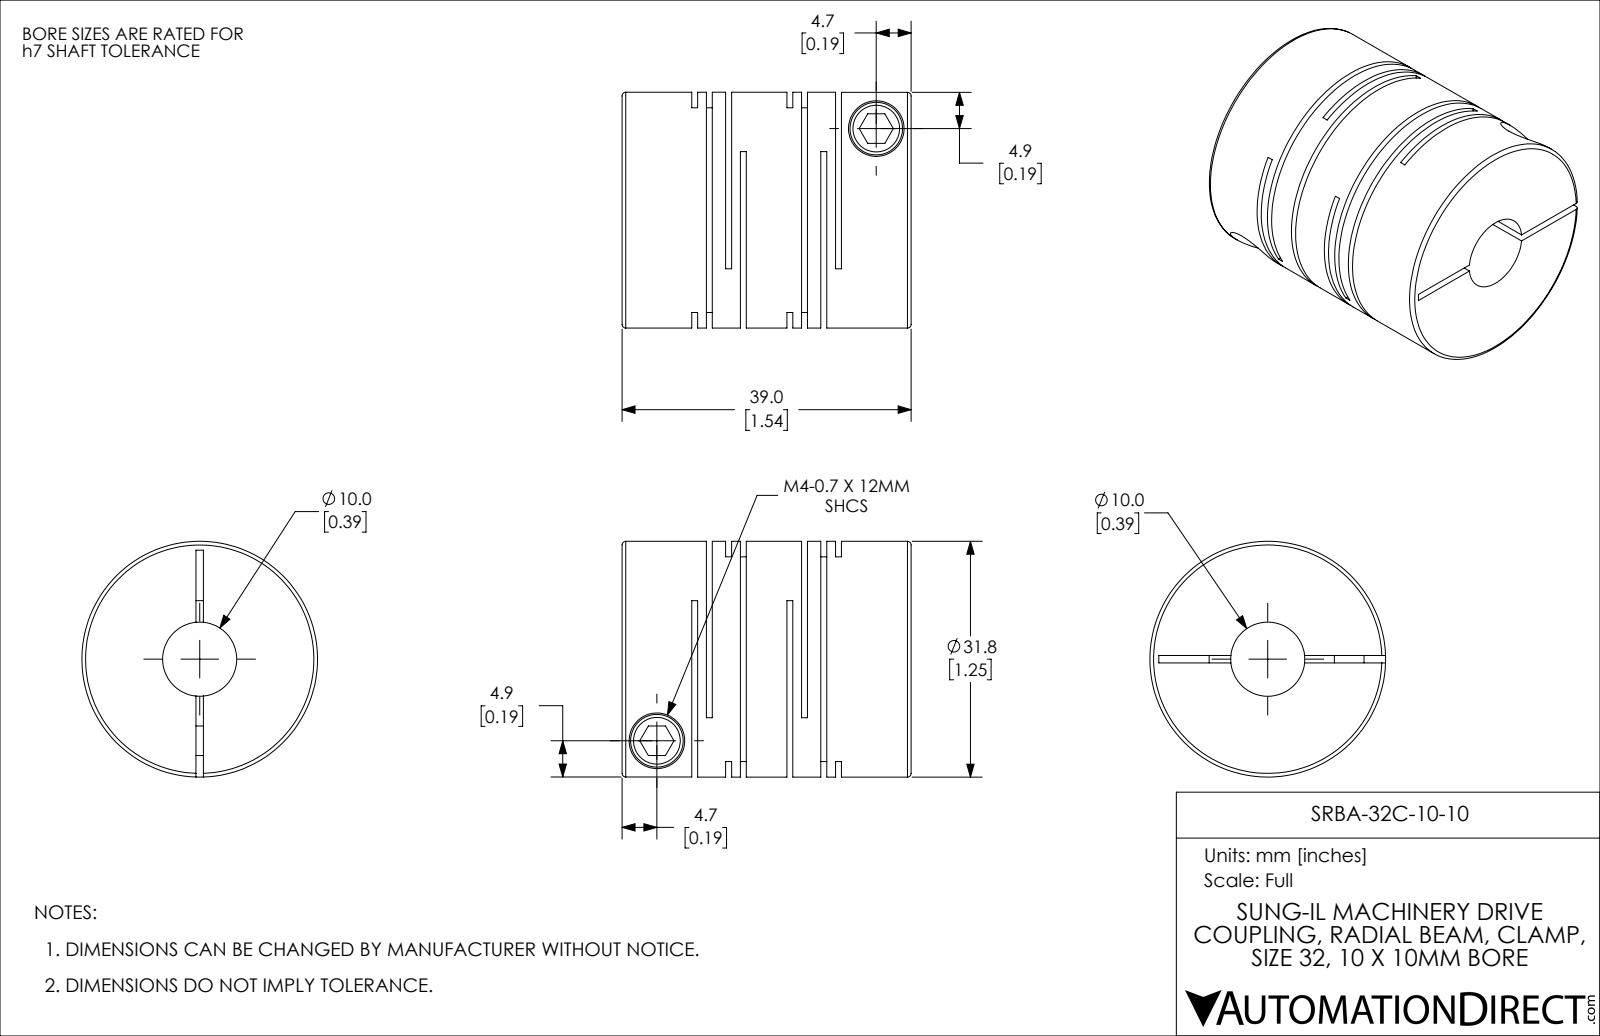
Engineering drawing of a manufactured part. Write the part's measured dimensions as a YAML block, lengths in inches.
part_name: "SRBA-32C-10-10"
step_written_by: "SolidWorks 2021 (CONFIG_CONTROL_DESIGN)"
units: inches
bodies: {solids: 1, faces: 114, planar: 60, cylindrical: 42, other: 12}
overall_size: [1.535, 1.252, 1.252]
volume: 1.431
surface_area: 25.12
round_holes:
  - {diameter: 0.157, count: 2}
  - {diameter: 0.295, count: 2}
  - {diameter: 0.394, count: 1}
round_bosses_or_shafts:
  - {diameter: 0.28, count: 2}
  - {diameter: 1.252, count: 1}
face_to_face_distances: [0.031, 0.506, 0.078, 0.18, 0.474, 0.046, 0.428, 0.149, 0.325, 0.102]
